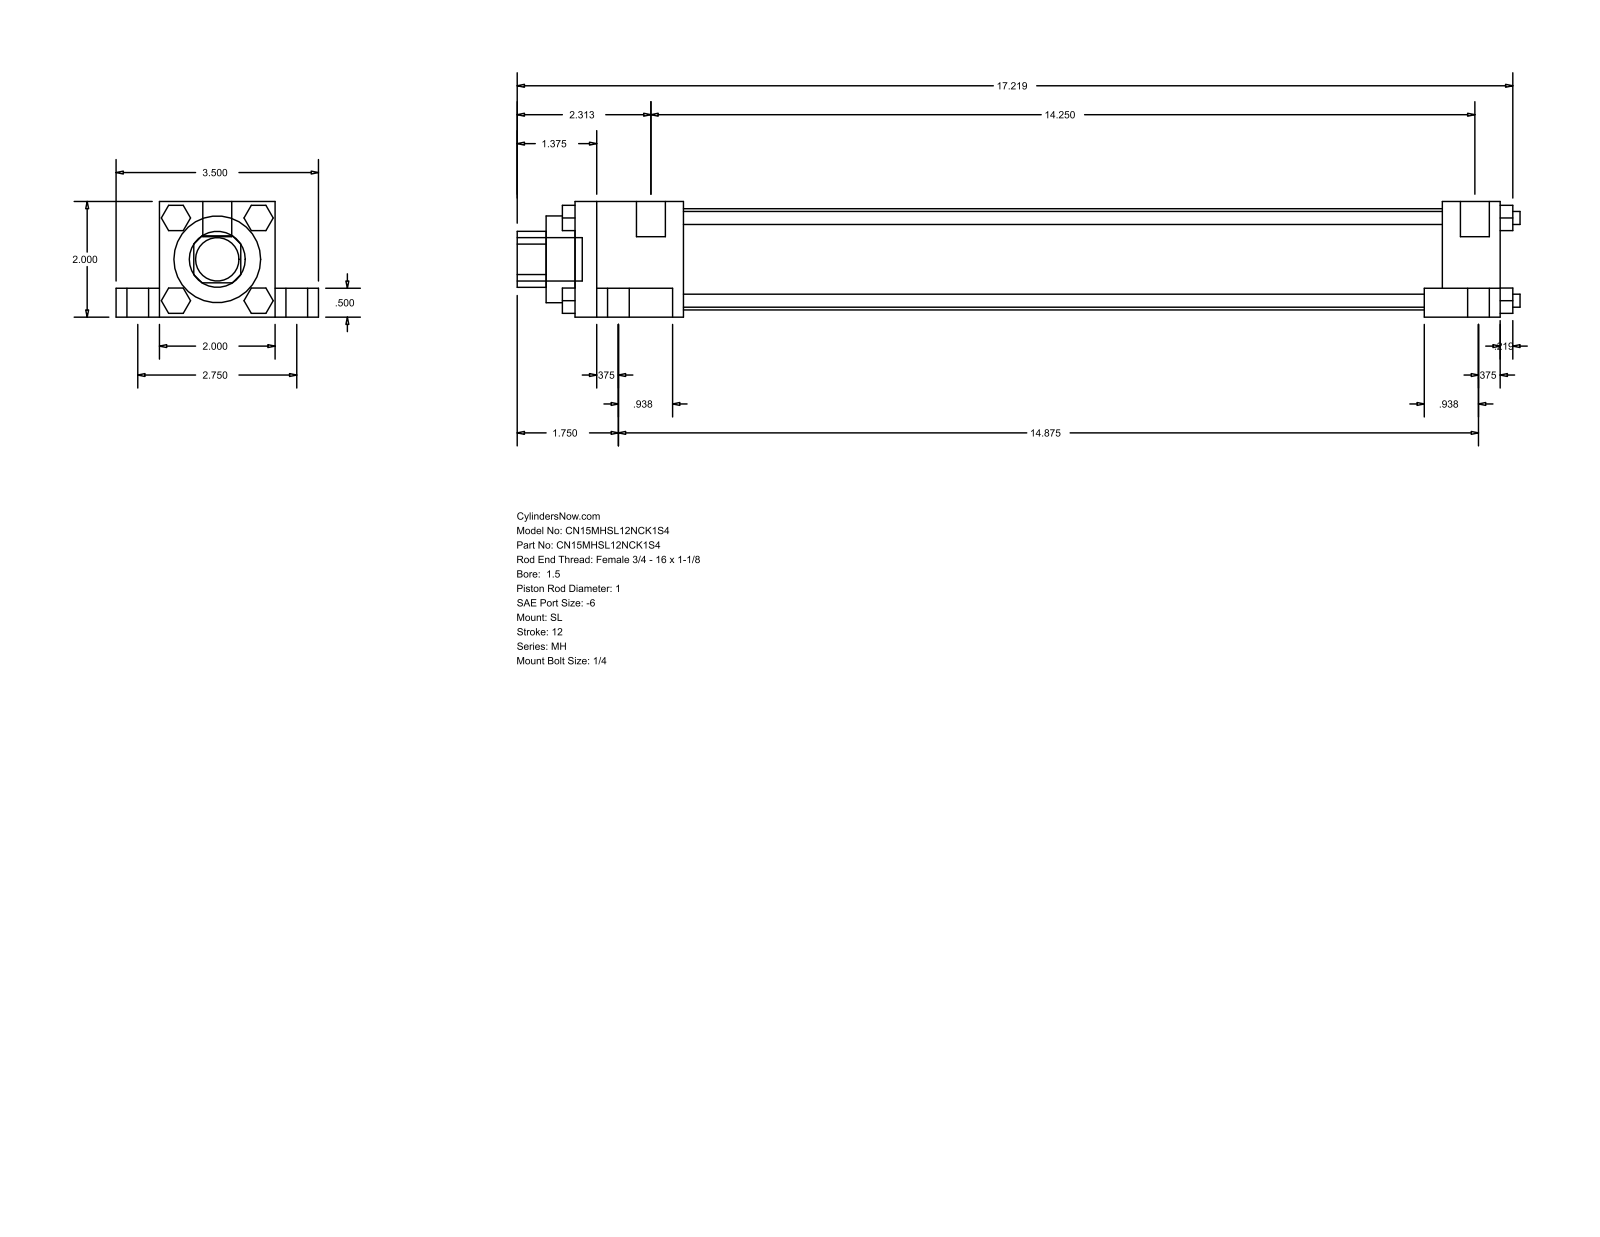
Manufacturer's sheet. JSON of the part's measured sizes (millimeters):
{"part_name": "MH_SL__0150_1", "step_written_by": "GSSL Pune (CONFIG_CONTROL_DESIGN)", "units": "millimeters", "bodies": {"solids": 0, "faces": 148, "planar": 112, "cylindrical": 36, "other": 0}, "overall_size": [440.53, 88.9, 50.8], "round_holes": [[25.4, 1], [38.1, 1], [44.45, 1]], "round_bosses_or_shafts": [[15.88, 4], [9.53, 4], [5.71, 4], [5.56, 4], [12.7, 2], [19.05, 1]], "partial_cylinders_radius": [[12.29, 1]], "face_to_face_distances": [50.8, 12.7, 38.1, 19.05, 69.85, 406.4, 25.4, 9.52, 33.34, 363.54]}
